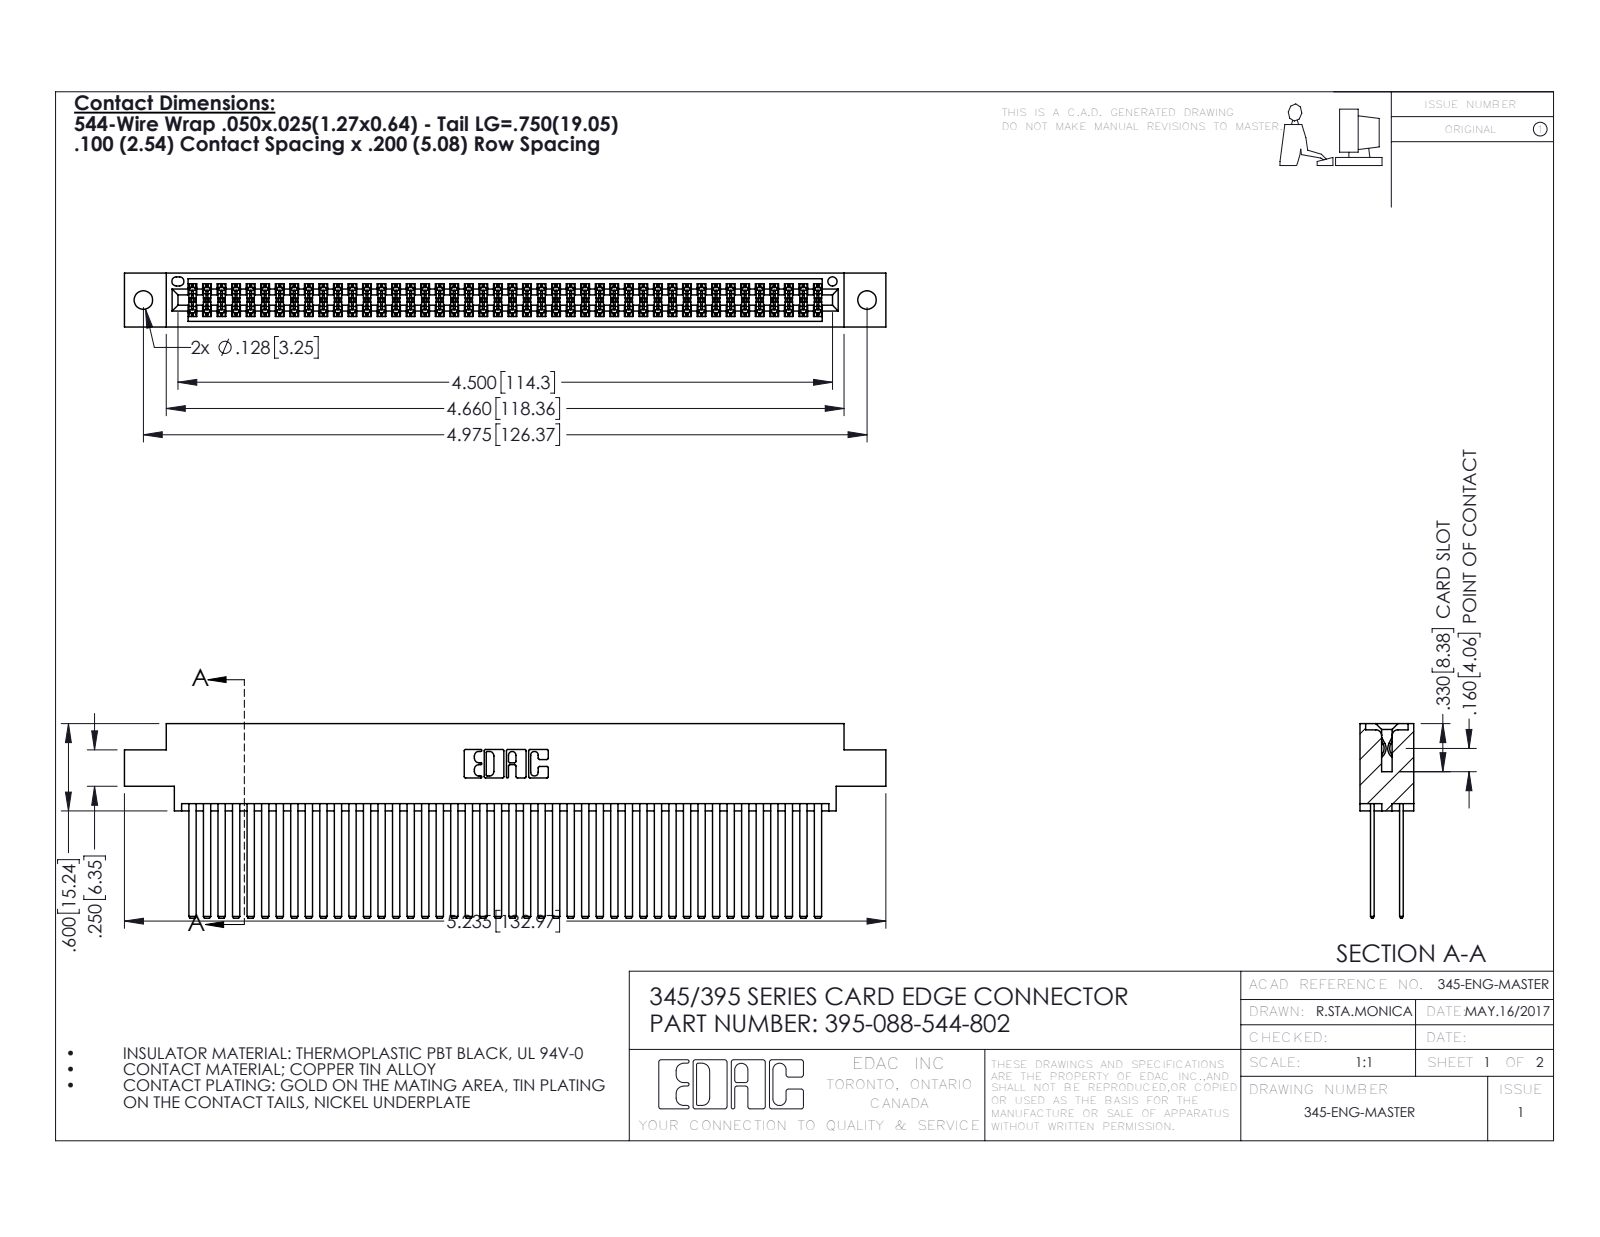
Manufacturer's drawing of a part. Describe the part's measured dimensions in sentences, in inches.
The part is named "345-292-001_345-293-144; 395-088-544-802; 345 Part_0.170 Offset - 0.128 Dia". Its 3-D file was written by "SolidWorks 2016 (CONFIG_CONTROL_DESIGN)". It is 89 solids with 4002 faces: 2636 planar, 1366 cylindrical and 0 other. Overall it measures 5.235 by 1.337 by 0.37 inches. Its volume is 0.855 cubic inches and its surface area 37.58 square inches. Round holes: 2 of diameter 0.128, 1 of diameter 0.064. Partial cylindrical surfaces (rounded edges, fillets, slot ends): 132 of radius 0.006, 22 of radius 0.01, 6 of radius 0.007, 6 of radius 0.031, 3 of radius 0.026, 2 of radius 0.014, 2 of radius 0.019, 2 of radius 0.022. The main face-to-face distances are 0.2, 0.025, 0.298, 0.072, 0.098, 0.272, 0.225, 0.175, 0.37, 0.15. The hole center spacings are 0.27, 4.739, 4.975.
